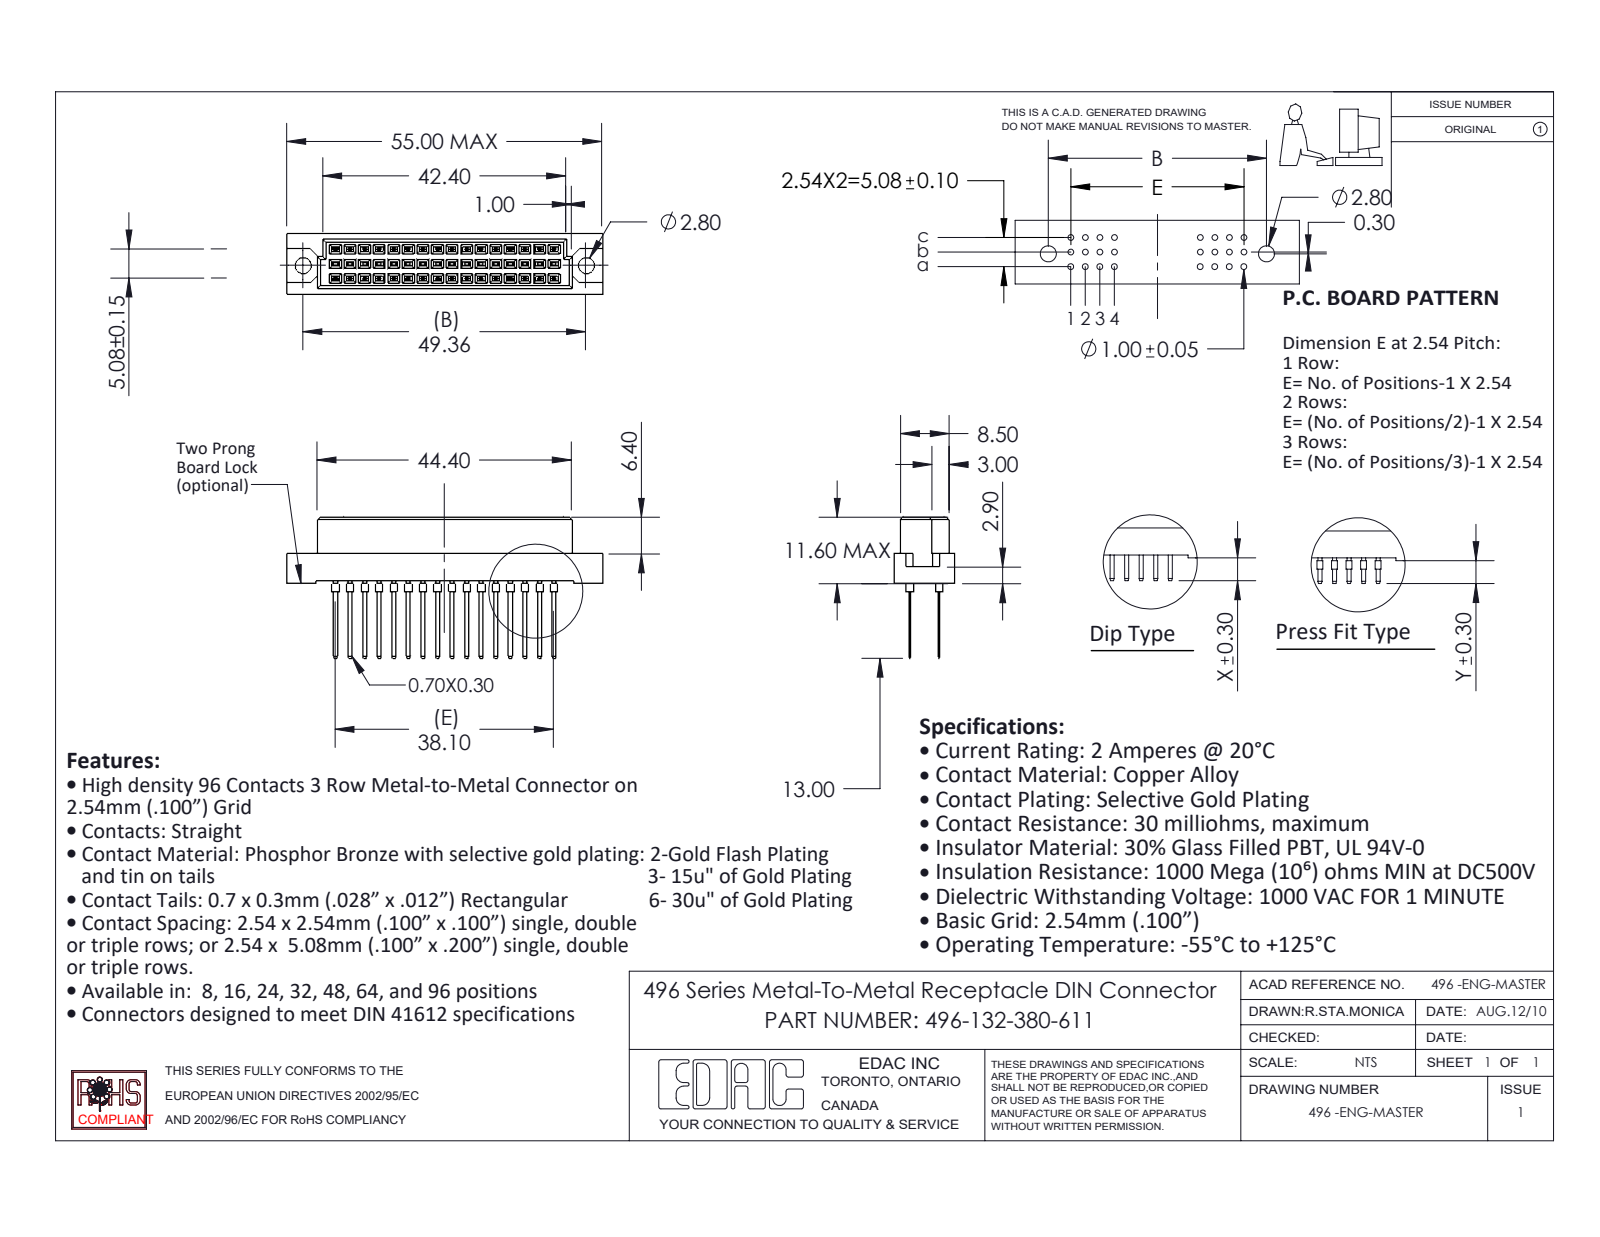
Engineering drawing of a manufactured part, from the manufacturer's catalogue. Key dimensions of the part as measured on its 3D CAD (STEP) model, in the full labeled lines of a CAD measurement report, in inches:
Part name (STEP PRODUCT): 496-290_80; 496 Part_48; 496-132-380-611
STEP written by: SolidWorks 2020 (CONFIG_CONTROL_DESIGN)
Units: inches
Bodies: 33 solids, 1242 faces (1174 planar, 68 cylindrical, 0 other)
Overall size (bounding box): 2.165 × 0.969 × 0.417
Volume: 0.289 in³ · Surface area: 8.395 in²
Round holes (diameter × count): ⌀0.11 ×2
Round bosses / shafts (diameter × count): ⌀0.039 ×32
Main face-to-face distances: 0.1, 0.2, 0.041, 0.376, 0.103, 0.115, 0.303, 0.315, 0.061, 0.073
Hole centre spacings: 1.943
